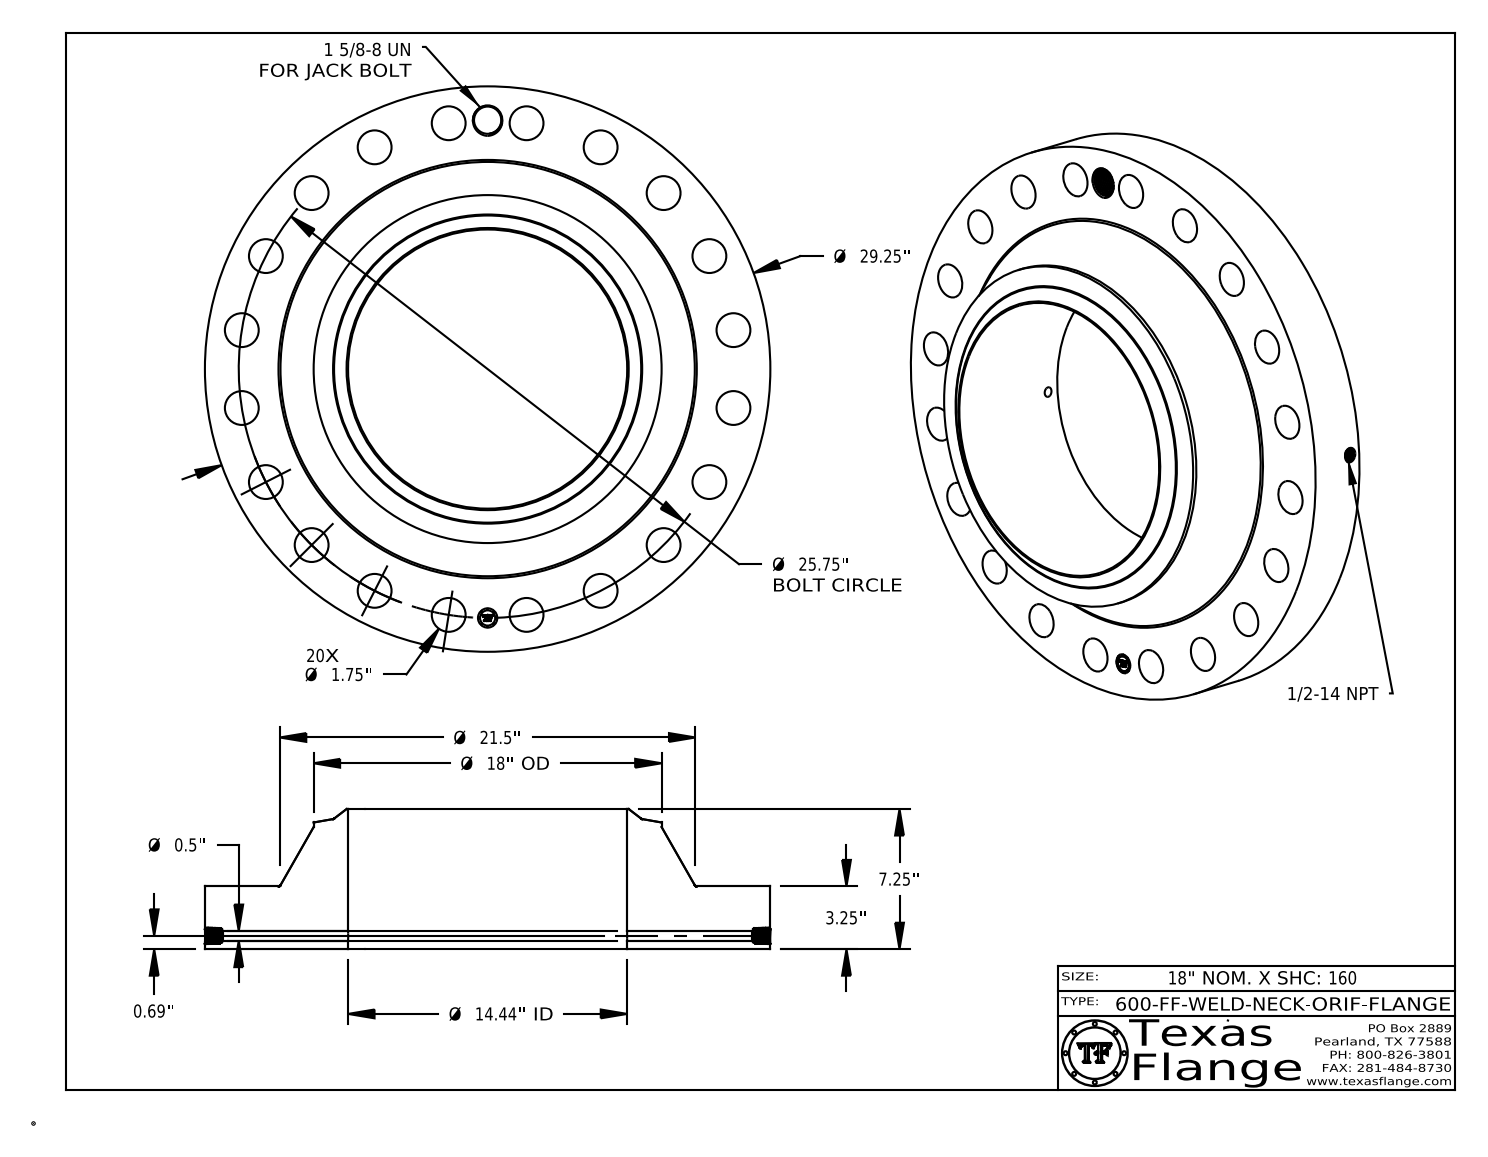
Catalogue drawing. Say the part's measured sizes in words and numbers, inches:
The part is named "600-FF-WELD-NECK". Its 3-D file was written by "CATIA V5 STEP AP214 (AUTOMOTIVE_DESIGN)". It is 1 solid with 860 faces: 368 planar, 137 cylindrical and 355 other. Overall it measures 29.25 by 29.25 by 7.25 inches. Its volume is 1 969 cubic inches and its surface area 2 091 square inches. Round holes: 20 of diameter 1.75, 1 of diameter 0.5, 1 of diameter 0.672, 1 of diameter 1, 1 of diameter 1.409, 1 of diameter 14.438. Round bosses or shafts: 8 of diameter 0.061, 1 of diameter 29.25, 1 of diameter 18, 1 of diameter 0.788. The main face-to-face distances are 3.25, 7.25, 4, 0.015, 3.235, 4.015, 0.298, 0.292, 0.054, 0.248. The hole center spacings are 15.135, 24.49, 25.433, 12.875, 11.69, 4.028, 7.957, 18.208.
